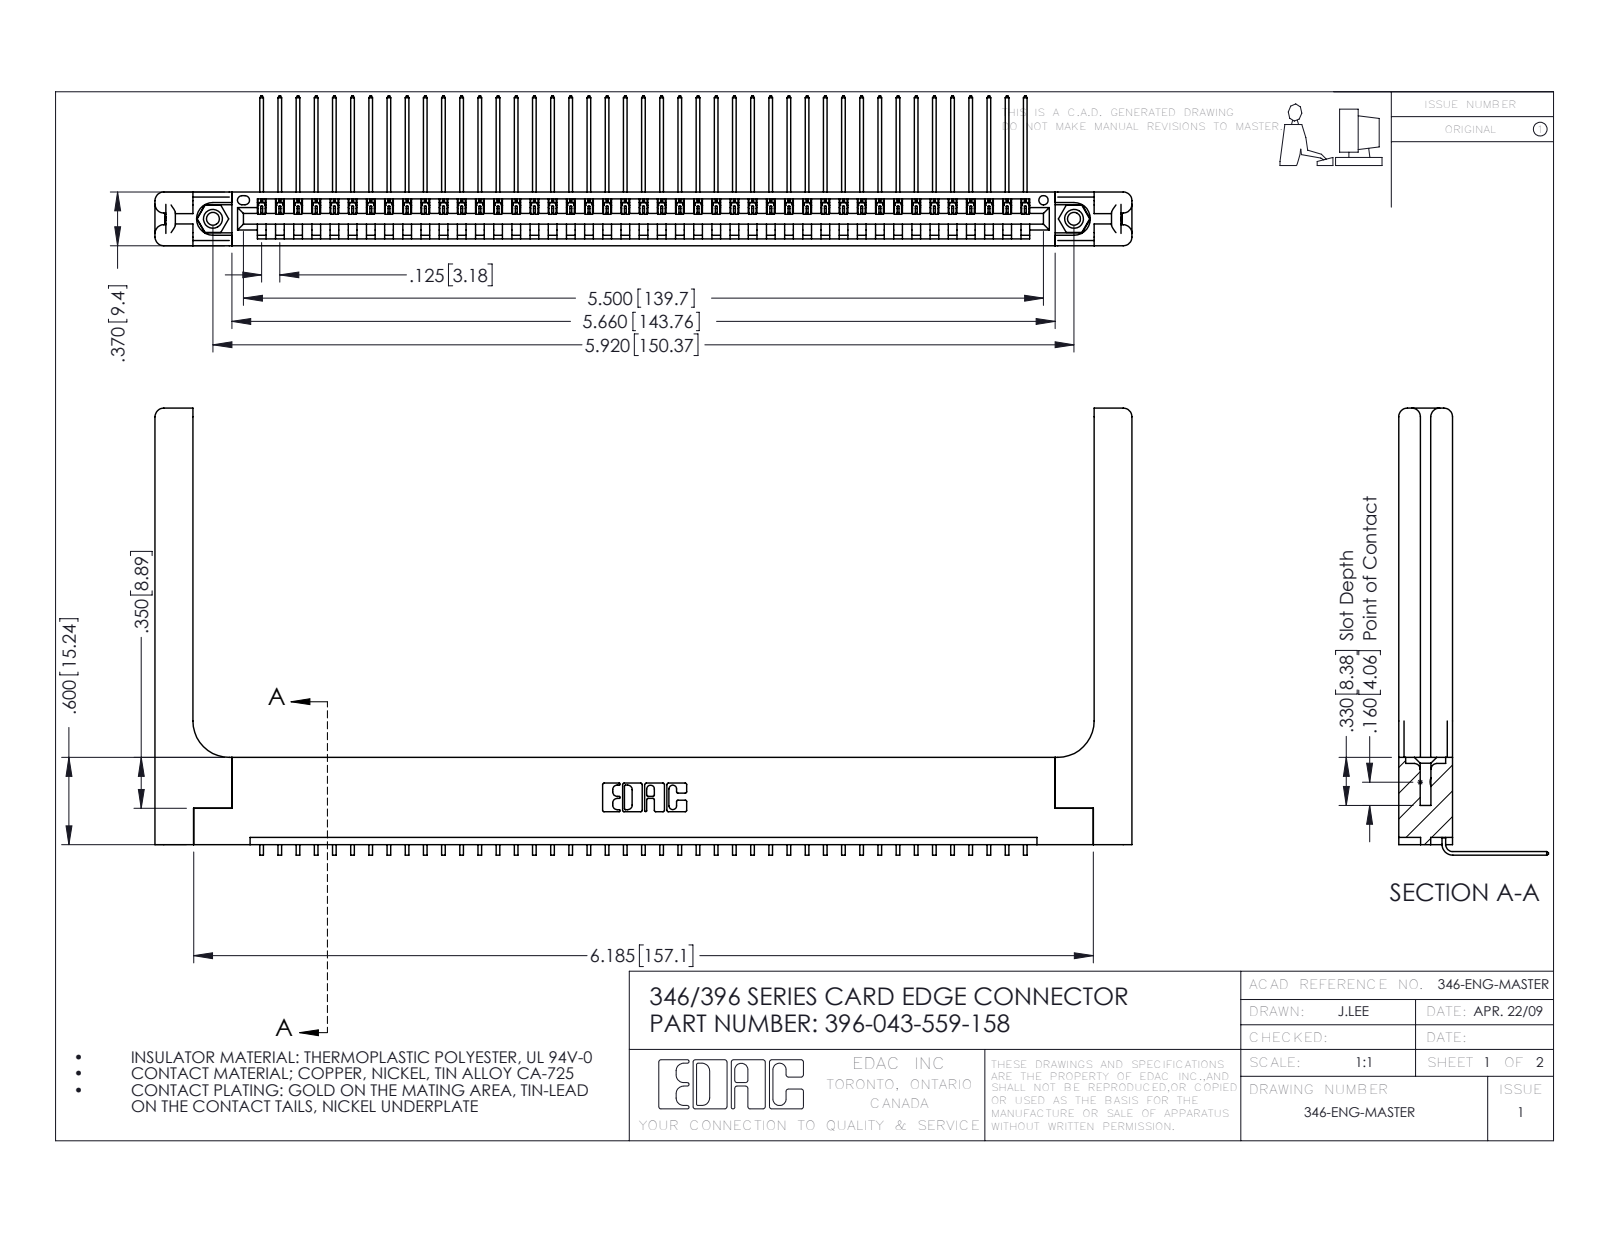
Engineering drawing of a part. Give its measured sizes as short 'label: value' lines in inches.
name: 346-220-058_345-220-058; 345-292-001_558 559 Tail - 1; 396-043-559-158; 345-250-001_345-250-001-102 (+1 more)
written by: SolidWorks 2016 (CONFIG_CONTROL_DESIGN)
unit: in
bodies: 48 solids, 2958 faces (2030 planar, 868 cylindrical, 60 other)
size: 6.716 × 3.073 × 1.03
volume: 1.464 in³; area: 41.28 in²
holes: 2× ⌀0.089, 2× ⌀0.125, 2× ⌀0.156, 1× ⌀0.064
bosses: 2× ⌀0.155
rounds: 86× R0.006, 22× R0.01, 16× R0.06, 6× R0.007, 6× R0.031, 3× R0.026, 2× R0.03, 2× R0.031
face distances: 0.37, 0.048, 0.322, 0.072, 0.148, 0.15, 0.025, 0.25, 0.298, 0.222
hole spacings: 0.246, 5.711, 5.92
